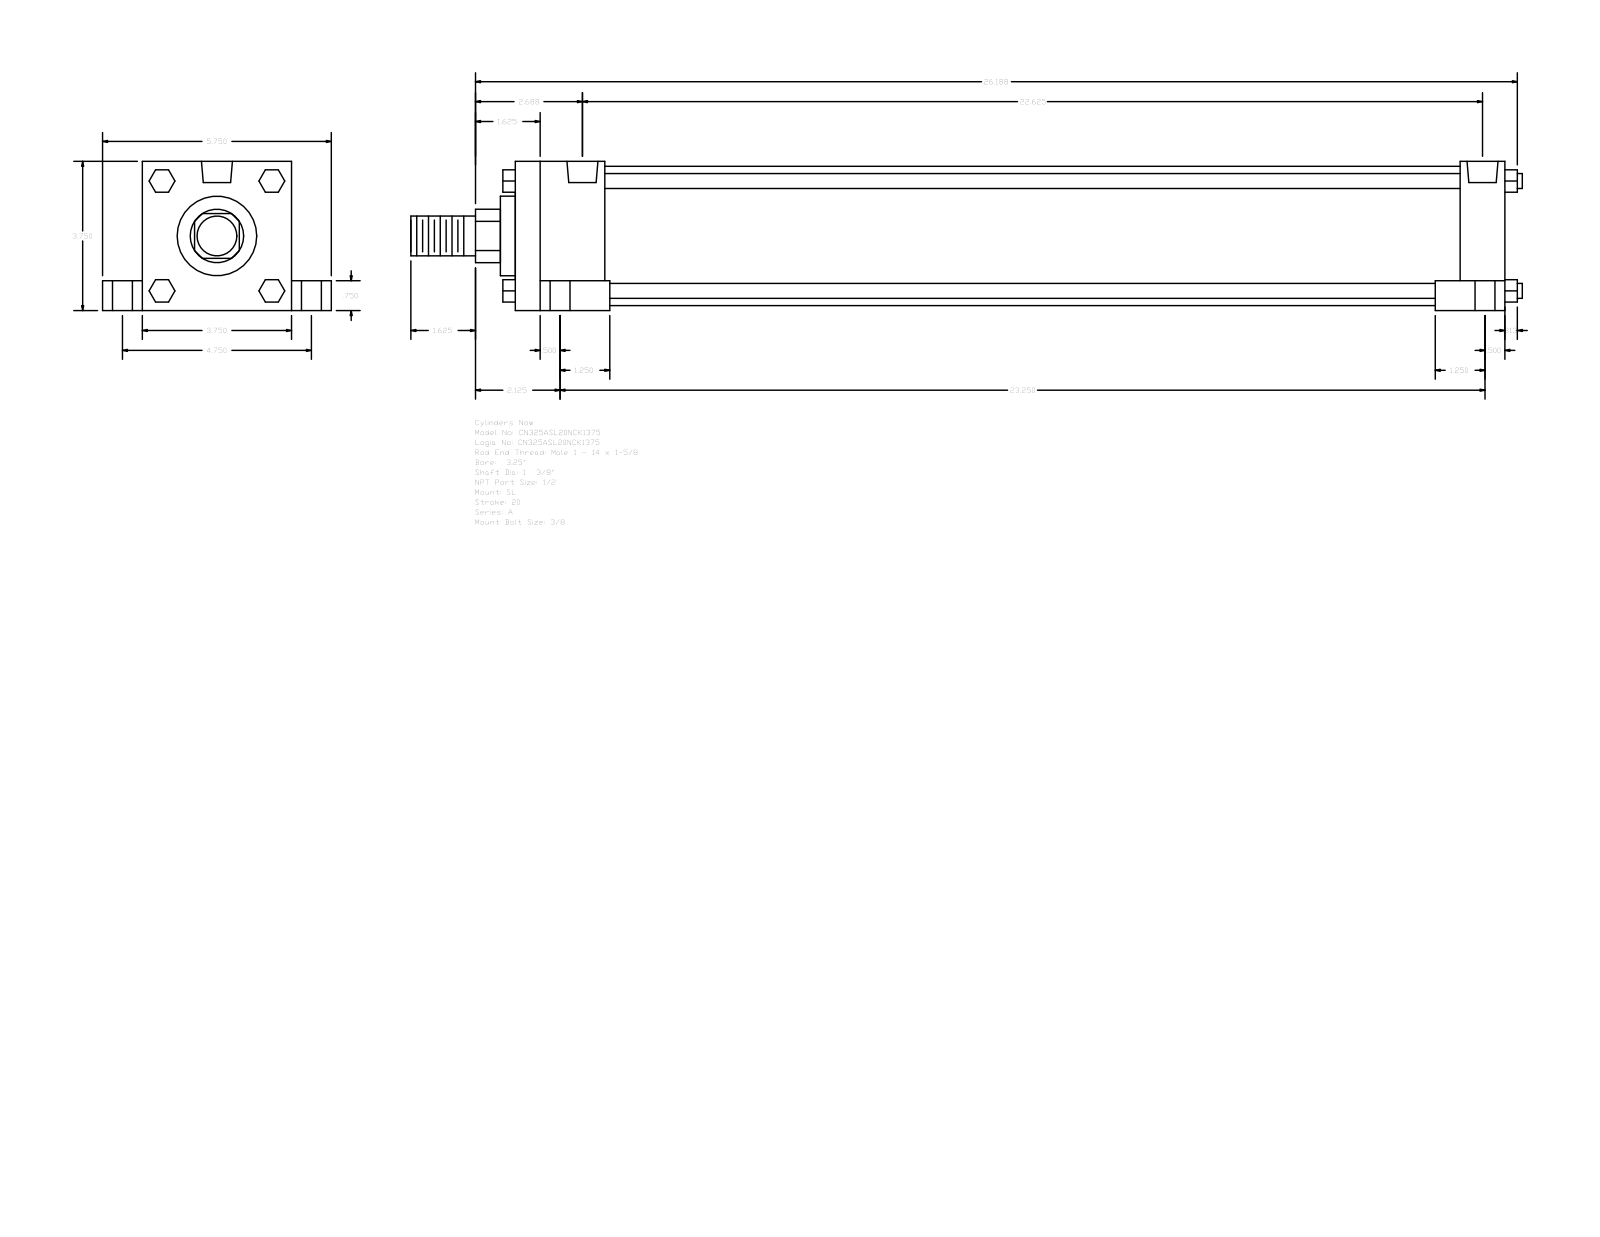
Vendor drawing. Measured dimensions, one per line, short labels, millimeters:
name: A_SL__0325_1.375
written by: GSSL Pune (CONFIG_CONTROL_DESIGN)
unit: mm
bodies: 0 solids, 150 faces (114 planar, 36 cylindrical, 0 other)
size: 709.61 × 146.05 × 95.25
holes: 4× ⌀8.73, 4× ⌀12.7, 4× ⌀19.05, 2× ⌀19.77
bosses: 4× ⌀9.53, 1× ⌀88.9, 1× ⌀50.8, 1× ⌀34.92, 1× ⌀25.4
rounds: 1× R17.06
face distances: 95.24, 631.83, 25.41, 120.65, 19.05, 76.19, 57.15, 28.58, 603.25, 546.1
hole spacings: 3.18, 60.35, 60.52, 62, 62.81, 120.66, 568.32, 571.5
